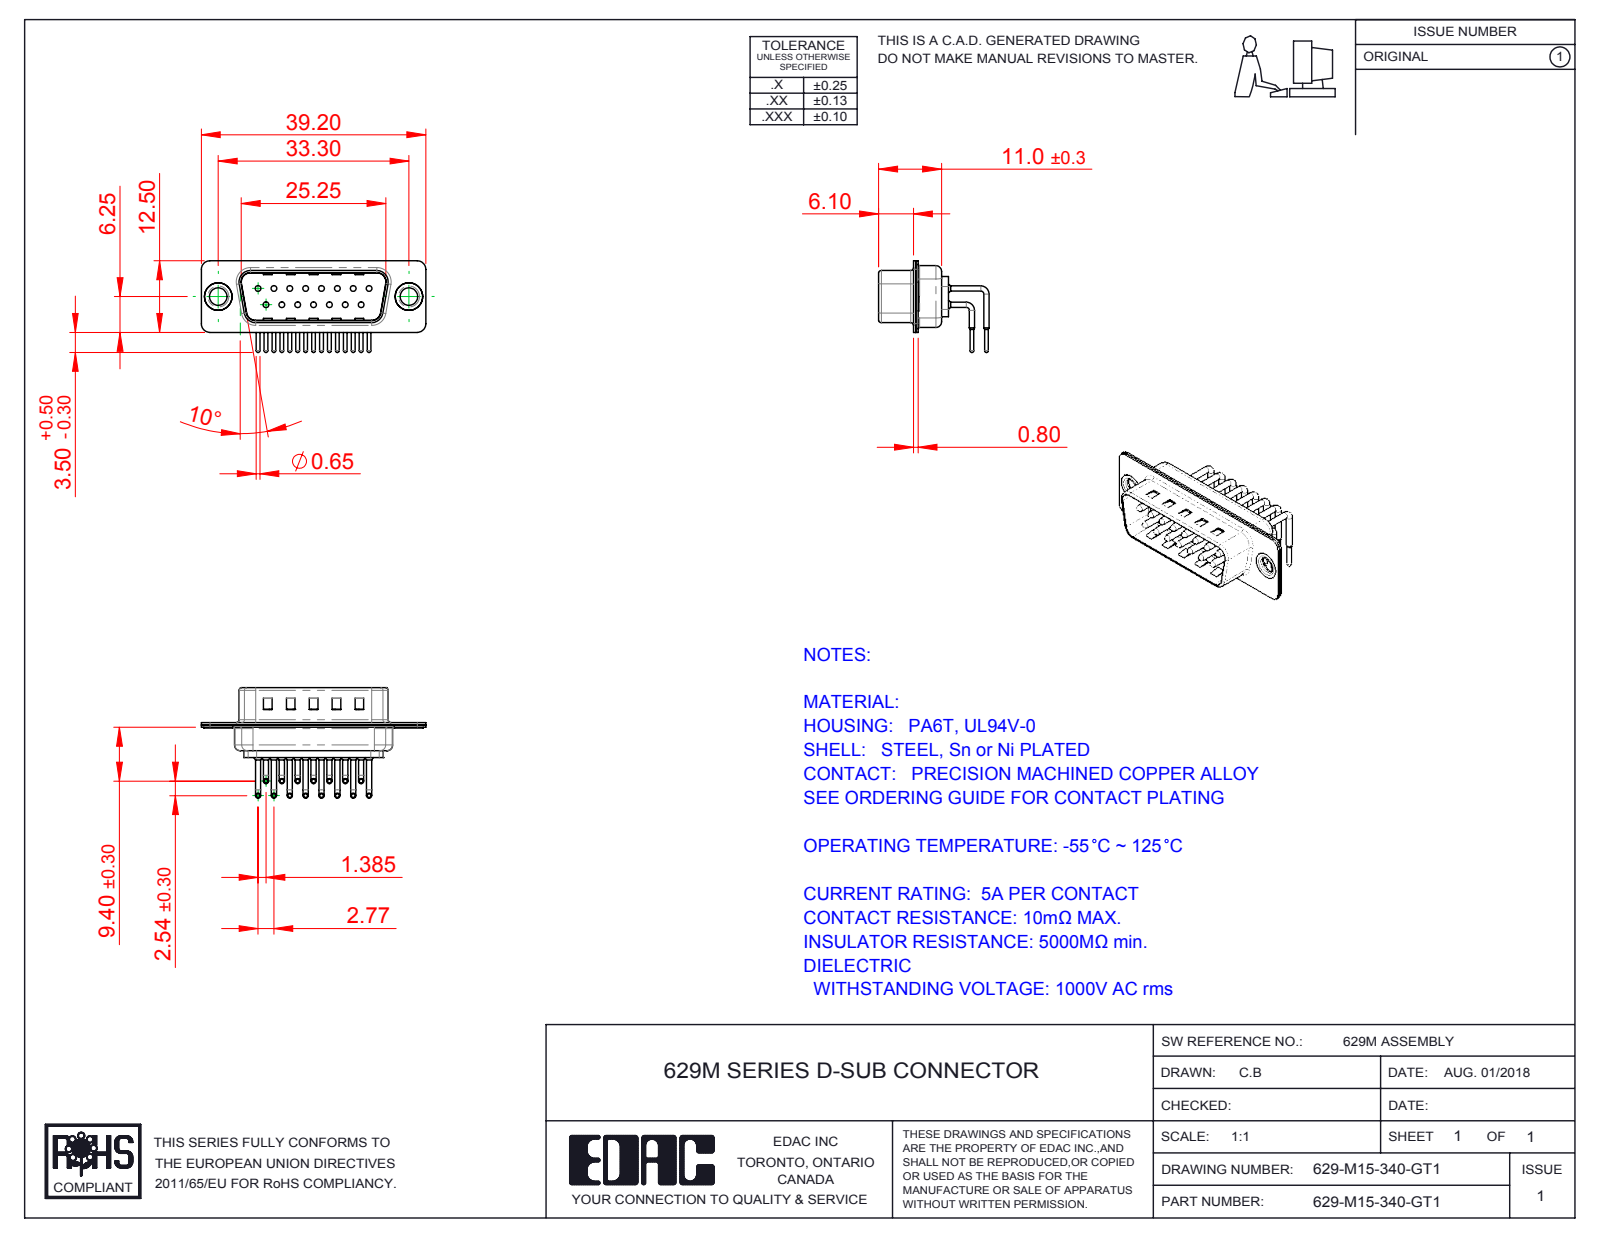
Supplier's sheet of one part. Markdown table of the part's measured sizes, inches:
| quantity | value |
| --- | --- |
| part name | 629-M15-340-GT1; 629M Contact Row 2; 629M Thru Hole Rivet; 629M Contact Row 1 (+3 more) |
| STEP written by | SolidWorks 2016 (CONFIG_CONTROL_DESIGN) |
| units | inches |
| bodies | 20 solids, 1964 faces (1099 planar, 657 cylindrical, 208 other) |
| overall size | 1.543 × 0.759 × 0.63 |
| volume | 0.115 in³ |
| surface area | 8.08 in² |
| round holes (diameter × count) | 0.039 × 15, 0.067 × 15, 0.079 × 15, 0.12 × 2, 0.157 × 2, 0.189 × 2 |
| round bosses / shafts (diameter × count) | 0.035 × 30, 0.059 × 15, 0.026 × 15, 0.197 × 2, 0.193 × 2, 0.14 × 2 |
| partial cylindrical surfaces (radius × count) | 0.059 × 16, 0.04 × 15, 0.079 × 12, 0.02 × 8, 0.063 × 8, 0.01 × 4, 0.024 × 4, 0.026 × 4 |
| main face-to-face distances | 0.016, 0.033, 0.376, 0.343, 0.049, 0.031, 0.409, 0.059, 0.014, 0.075 |
| hole center spacings | 0.124, 0.109, 0.218, 0.327, 0.436, 0.198, 0.198, 0.294 |
